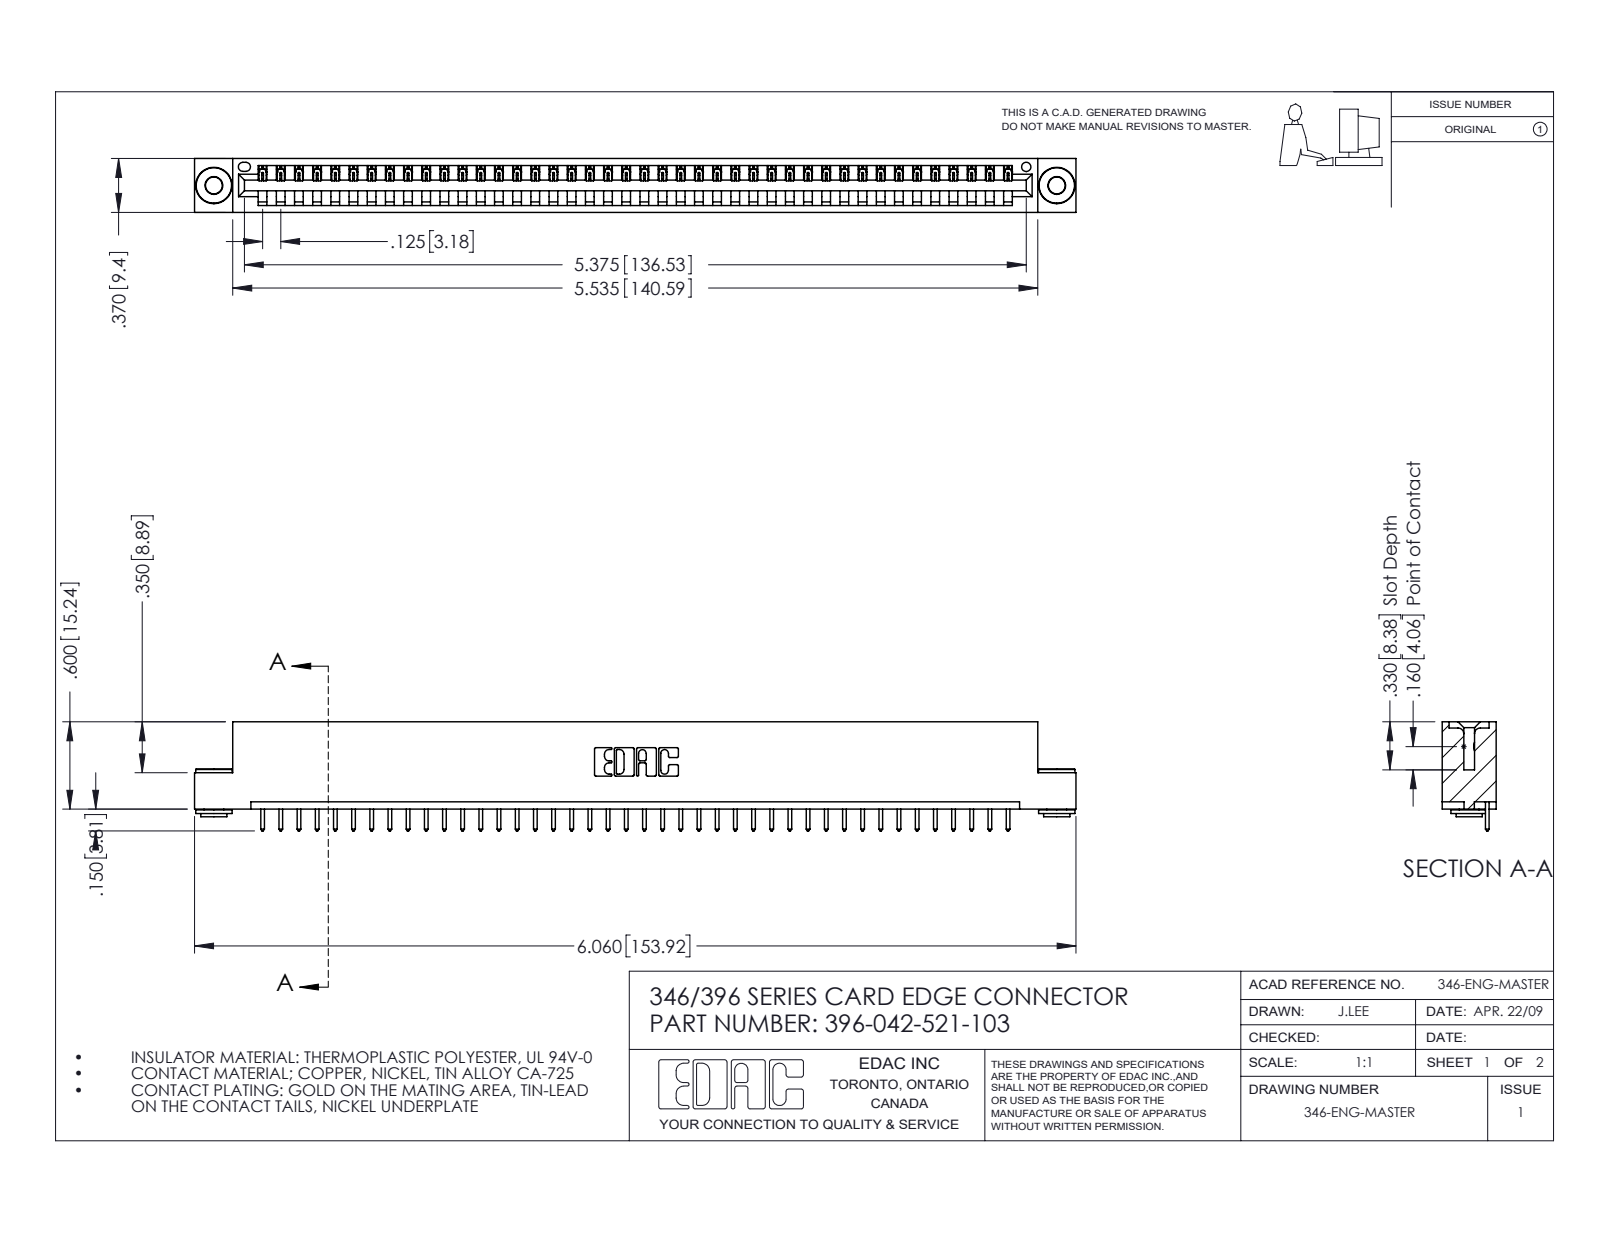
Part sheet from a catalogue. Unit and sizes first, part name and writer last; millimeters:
Units: millimetres
Overall size (bounding box): 153.9 × 19.1 × 9.4
Round holes (diameter × count): ⌀2.9 ×2, ⌀4 ×2, ⌀1.6 ×1
Round bosses / shafts (diameter × count): ⌀6.4 ×2, ⌀4.6 ×2, ⌀3.5 ×2
Partial cylindrical surfaces — rounded edges, fillets, slot ends (radius × count): R0.2 ×84, R0.3 ×84, R0.3 ×22, R0.2 ×6, R0.8 ×6, R0.7 ×3, R0.8 ×2, R1 ×2
Main face-to-face distances: 1.2, 8.2, 9.4, 6.4, 0.6, 1.8, 7.6, 3.8, 5.6, 2.5
Hole centre spacings: 6.2, 141.9, 147.2
Volume: 14 600 mm³ · Surface area: 18 030 mm²
Bodies: 45 solids, 2596 faces (1766 planar, 822 cylindrical, 8 other)
Part name (STEP PRODUCT): 345-292-001_345-293-121; 345-250-002_345-250-002-102; 346 Part_Flush Mounting Lugs - 0.156 Dia-TH; 396-042-521-103
STEP written by: SolidWorks 2016 (CONFIG_CONTROL_DESIGN)
